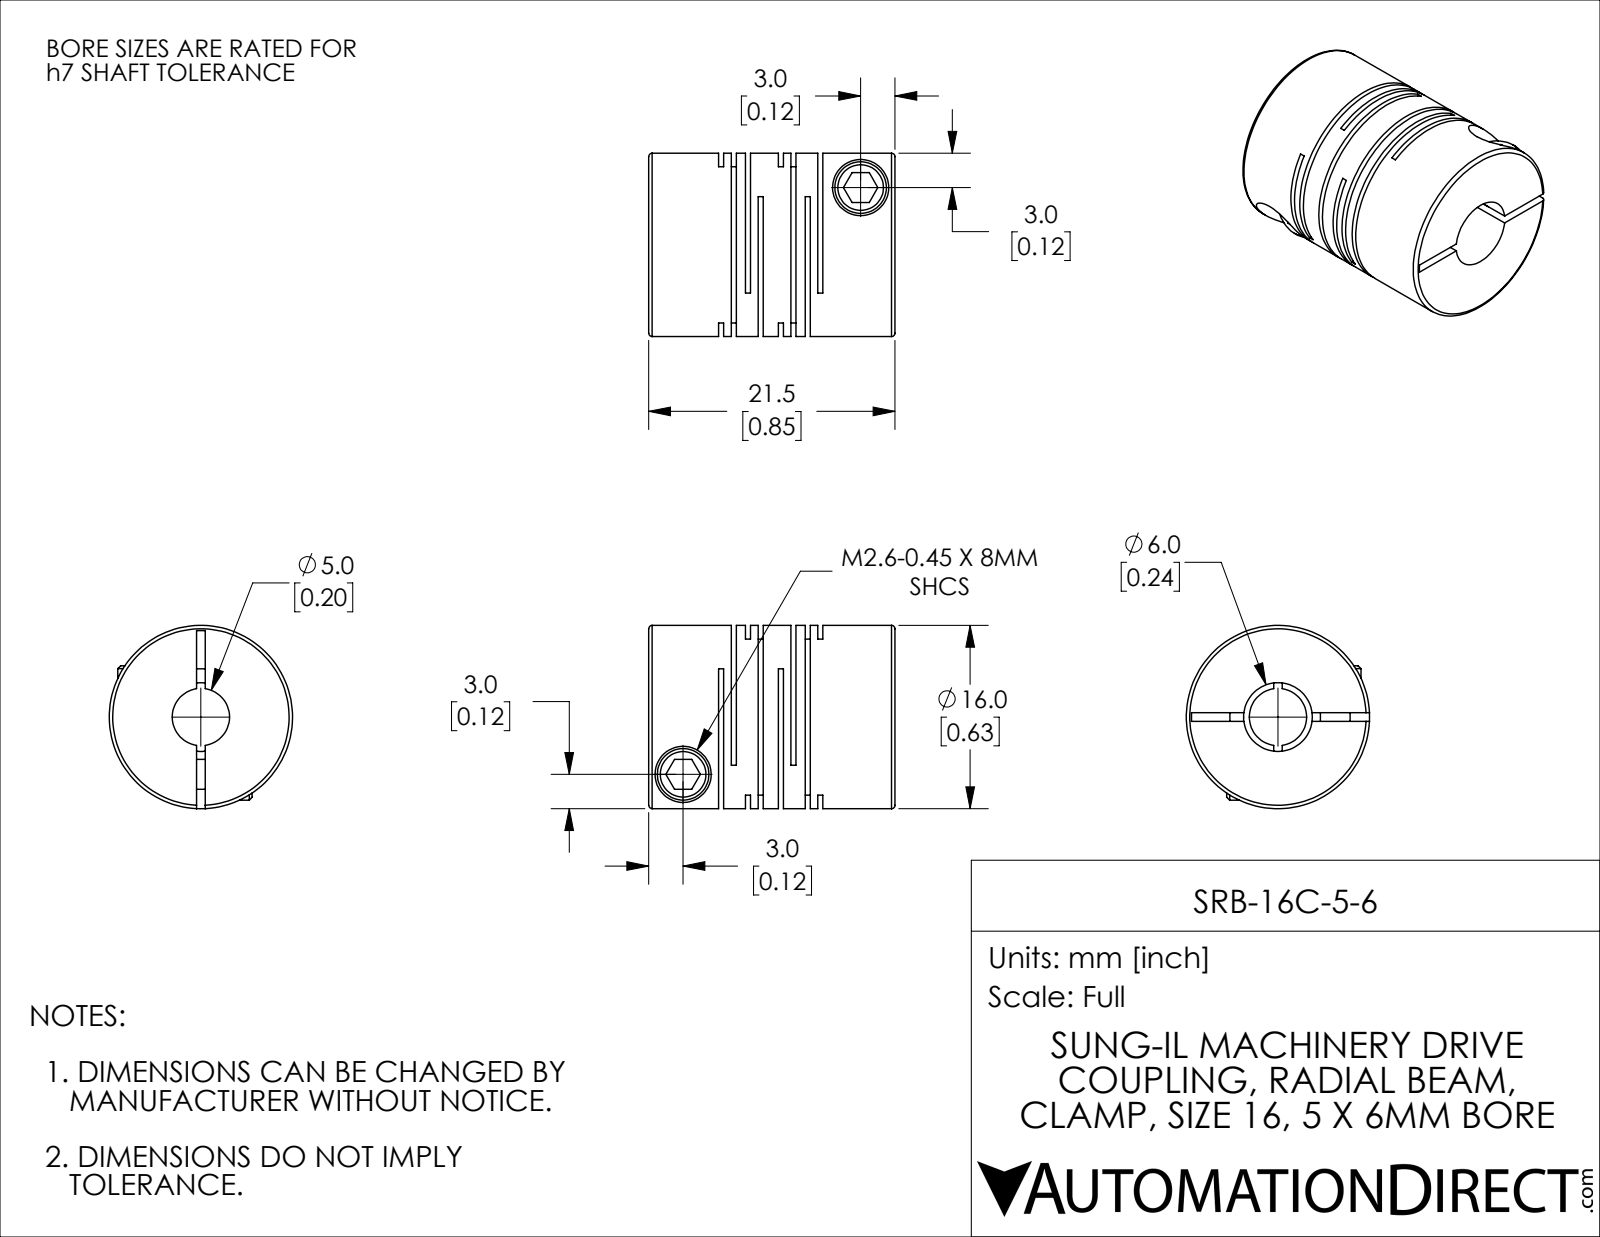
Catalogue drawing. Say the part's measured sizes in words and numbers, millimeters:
The part is named "SRB-16C-5-6". Its 3-D file was written by "SolidWorks 2021 (CONFIG_CONTROL_DESIGN)". It is 1 solid with 114 faces: 60 planar, 42 cylindrical and 12 other. Overall it measures 21.5 by 16 by 16 millimeters. Its volume is 3 101 cubic millimeters and its surface area 4 252 square millimeters. Round holes: 2 of diameter 2.6, 2 of diameter 4.9, 1 of diameter 5, 1 of diameter 6. Round bosses or shafts: 2 of diameter 4.5, 1 of diameter 16. The main face-to-face distances are 0.44, 1.1, 2.35, 5.21, 0.66, 1.91, 4.77, 1.25, 4.11, 2.86.
